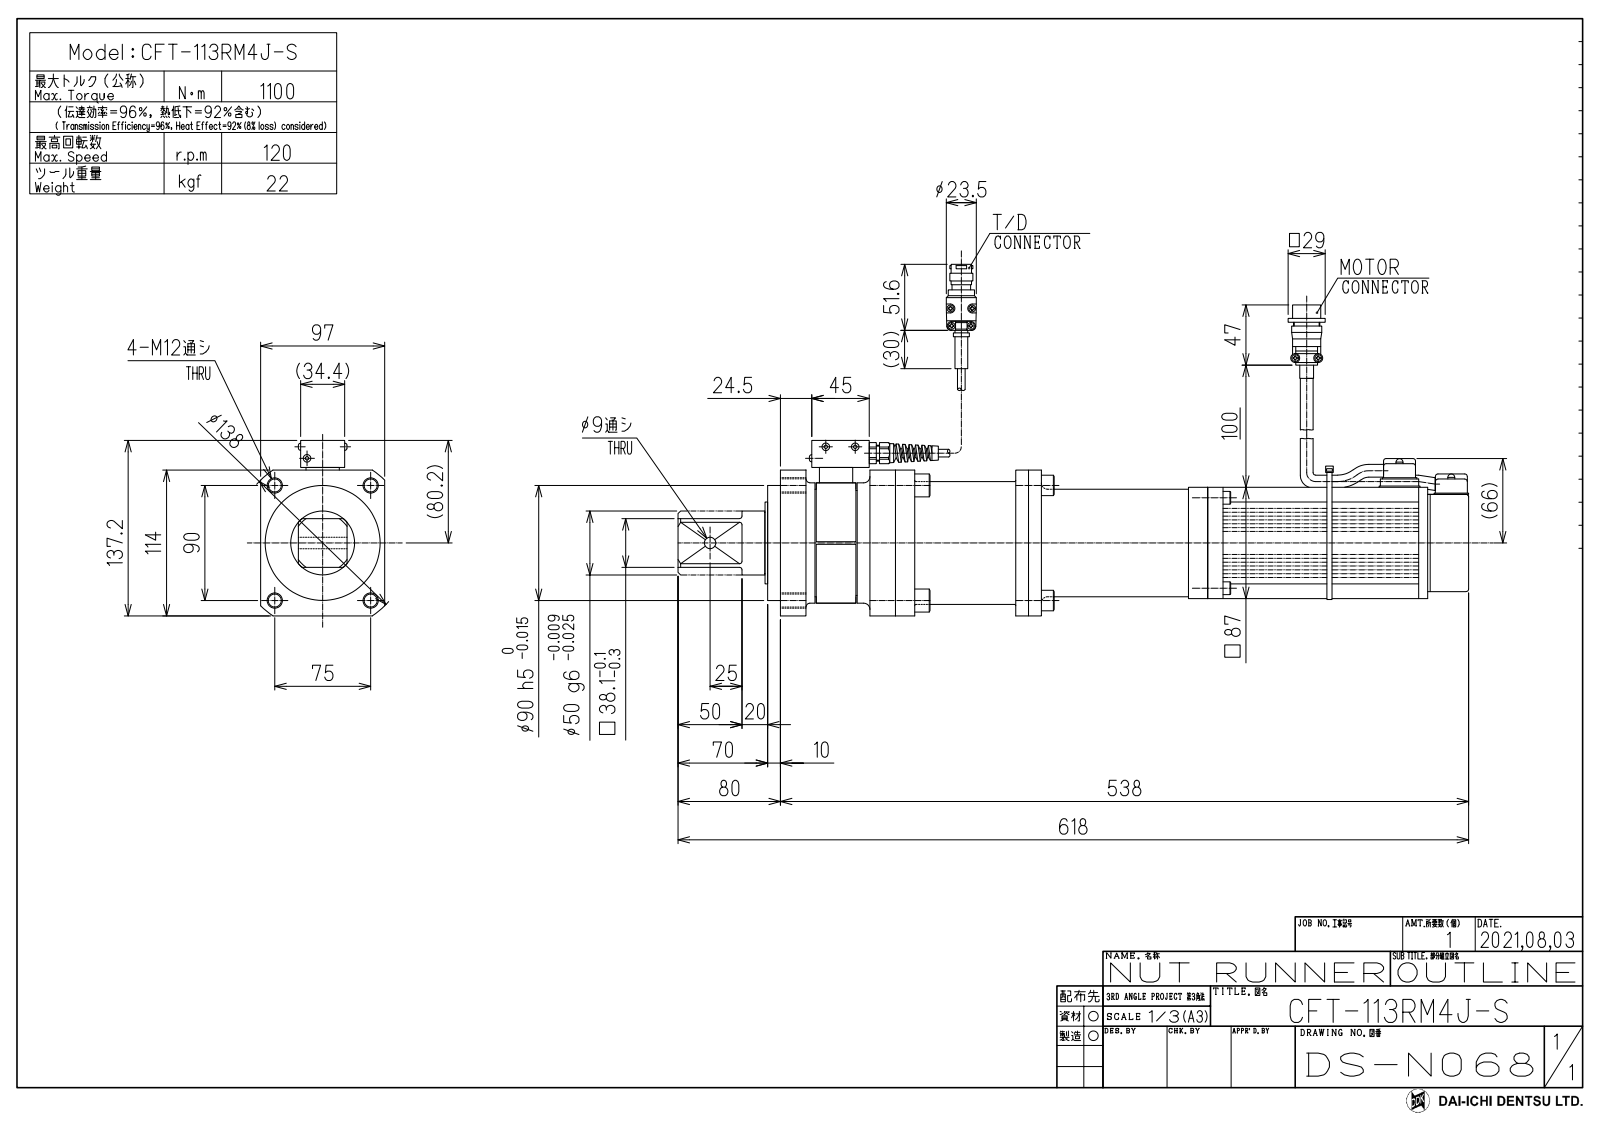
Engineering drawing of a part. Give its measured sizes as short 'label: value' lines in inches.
name: CFT-113RM4J-S(DS-N068)_OUTLINE_20210803
written by: Autodesk Inventor 2021 (AUTOMOTIVE_DESIGN)
unit: in
bodies: 1 solid, 1200 faces (698 planar, 275 cylindrical, 227 other)
size: 24.331 × 5.402 × 3.819
volume: 245.7 in³; area: 491.3 in²
holes: 4× ⌀0.197, 4× ⌀0.315, 4× ⌀0.335, 4× ⌀0.404, 4× ⌀0.472, 2× ⌀0.098, 1× ⌀0.059, 1× ⌀0.354, 1× ⌀3.18
bosses: 7× ⌀0.315, 5× ⌀0.276, 4× ⌀0.709, 4× ⌀0.63, 4× ⌀0.394, 4× ⌀0.335, 4× ⌀0.295, 3× ⌀0.224
rounds: 48× R0.024, 28× R0.039, 9× R0.02, 8× R0.079, 8× R0.118, 7× R0.059, 6× R0.197, 4× R0.012
face distances: 0.118, 0.059, 0.177, 0.236, 1.772, 1.594, 1.831, 3.425, 1.713, 1.535
hole spacings: 0.389, 1.969, 2.306, 2.784, 2.893, 3.165, 4.27, 1.091
